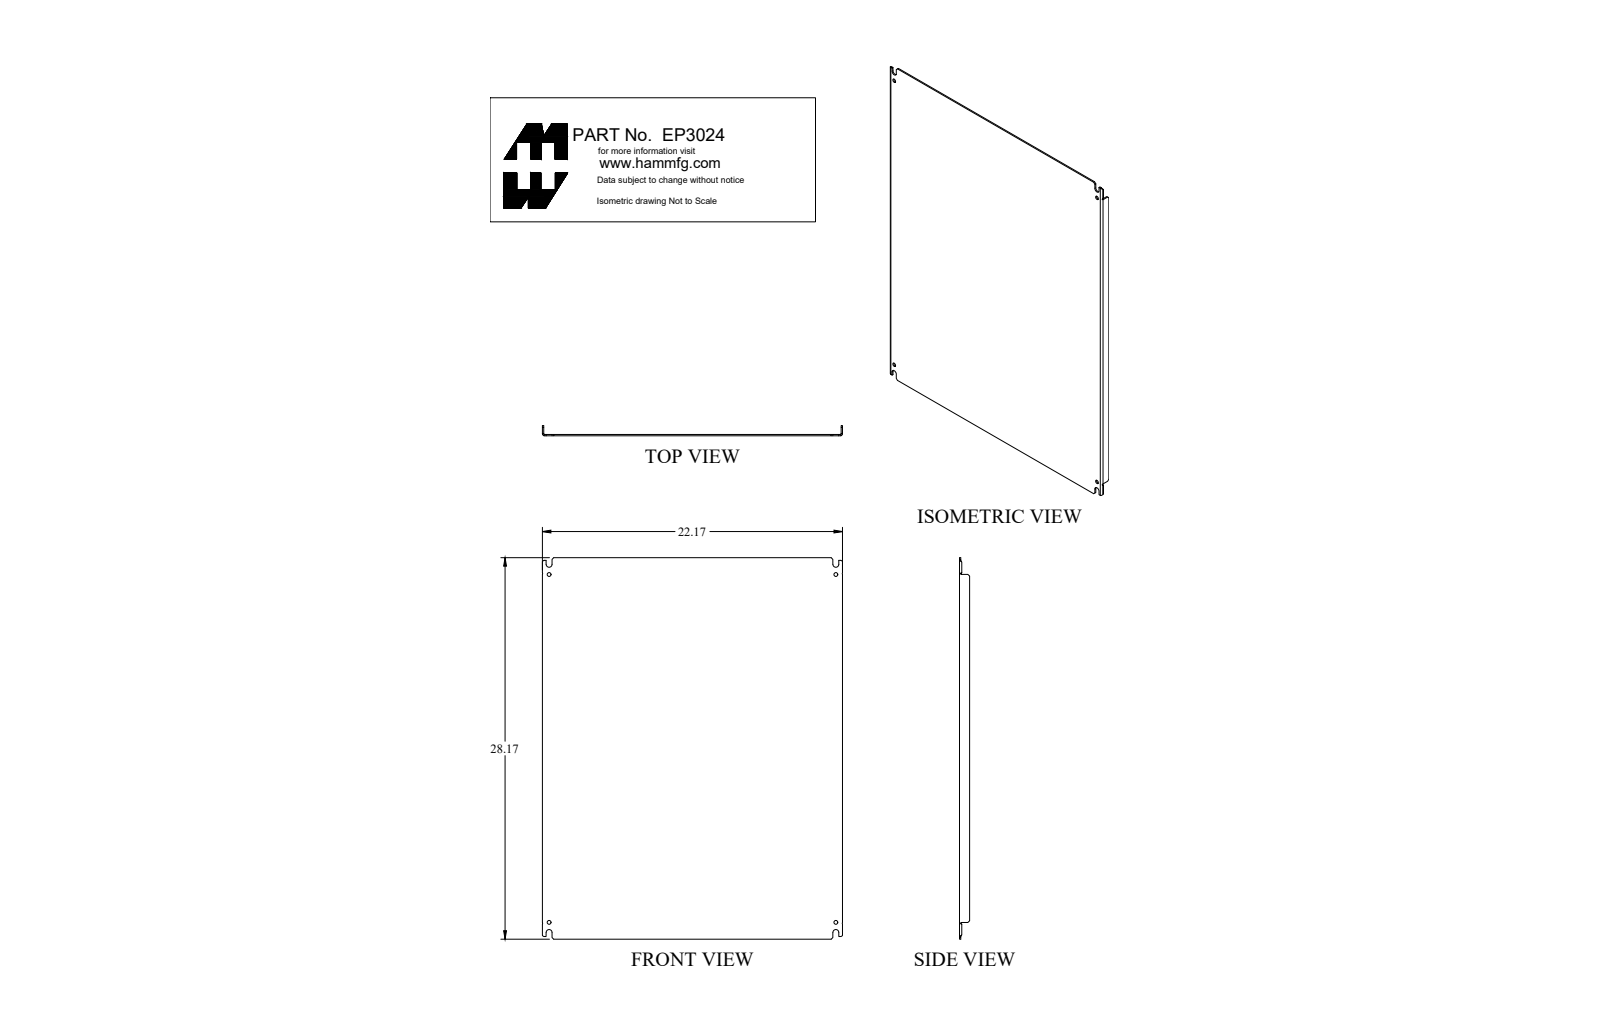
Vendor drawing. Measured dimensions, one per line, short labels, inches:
name: EP3024
written by: SolidWorks 2018 (AUTOMOTIVE_DESIGN)
unit: in
bodies: 1 solid, 84 faces (50 planar, 26 cylindrical, 8 other)
size: 28.17 × 22.17 × 0.75
volume: 62.18 in³; area: 1 319 in²
holes: 4× ⌀0.281
rounds: 4× R0.219, 2× R0.048, 2× R0.062, 2× R0.143
face distances: 0.095, 22.075, 21.98, 22.17, 0.75, 0.655, 28.17, 0.171, 0.076, 0.579
hole spacings: 21.188, 25.688, 33.299
